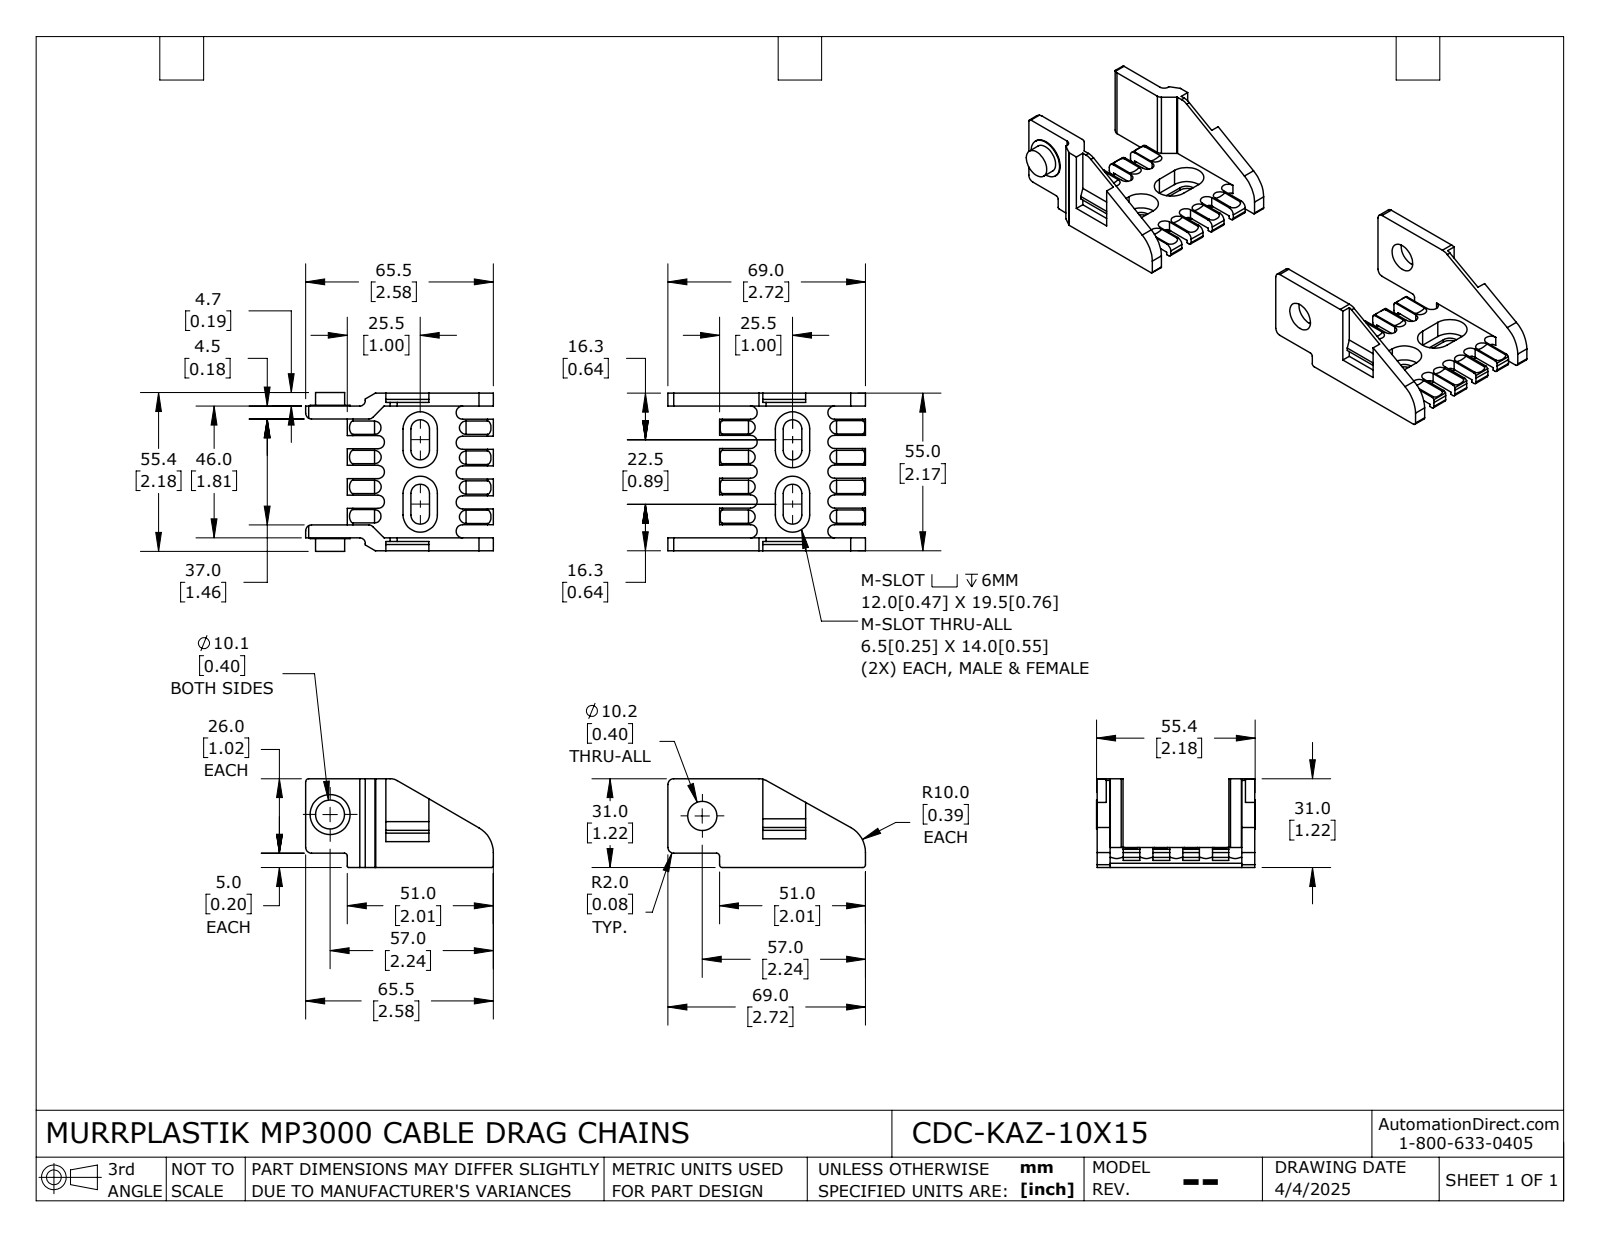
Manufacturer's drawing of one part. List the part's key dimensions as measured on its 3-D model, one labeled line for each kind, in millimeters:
Part name (STEP PRODUCT): CDC-KAZ-10X15
STEP written by: SolidWorks 2024 (AUTOMOTIVE_DESIGN)
Units: millimetres
Bodies: 2 solids, 382 faces (210 planar, 156 cylindrical, 16 other)
Overall size (bounding box): 195.5 × 55.4 × 31
Volume: 42 320 mm³ · Surface area: 26 902 mm²
Round holes (diameter × count): ⌀10.2 ×1
Round bosses / shafts (diameter × count): ⌀14 ×1, ⌀10.1 ×1
Partial cylindrical surfaces — rounded edges, fillets, slot ends (radius × count): R2.3 ×18, R1 ×13, R2 ×13, R7 ×9, R3.25 ×8, R6 ×8, R0.5 ×4, R0.1 ×2
Main face-to-face distances: 4.5, 50.5, 46, 55, 7, 3.5, 9, 5.8, 41.5, 1
